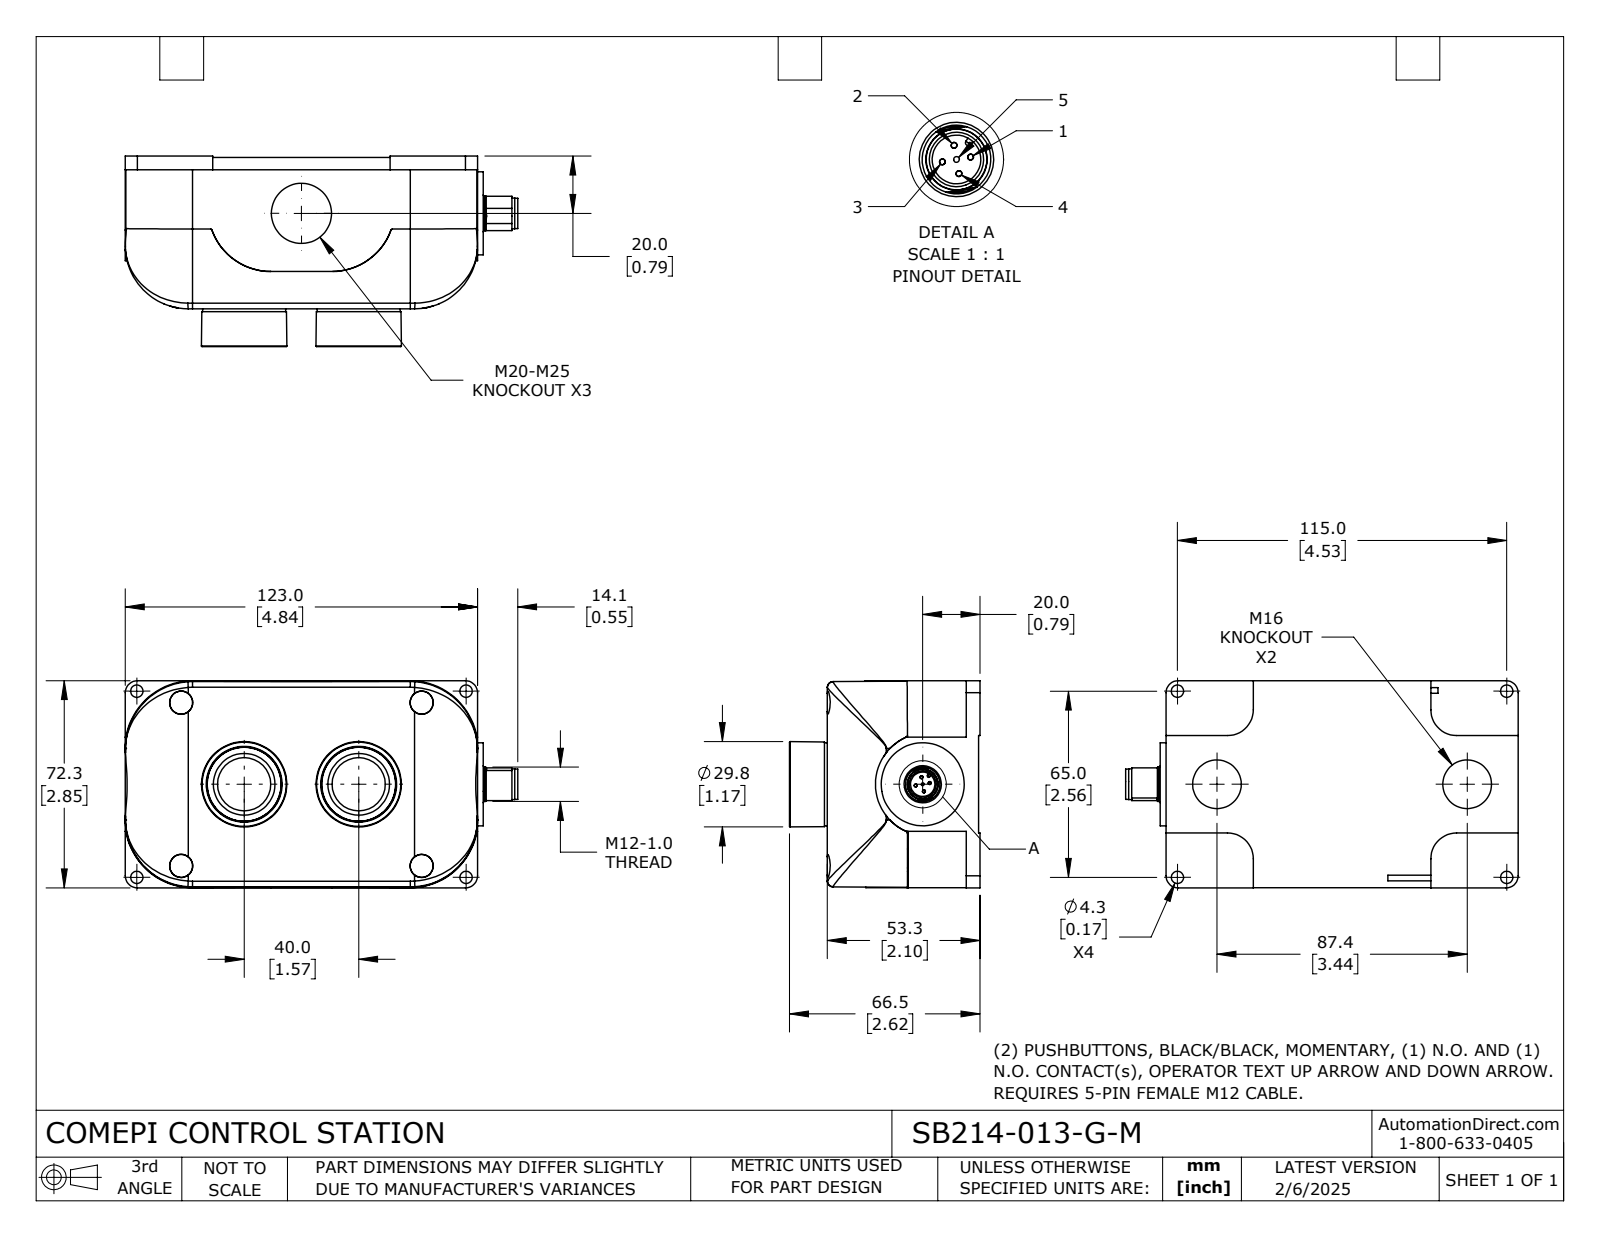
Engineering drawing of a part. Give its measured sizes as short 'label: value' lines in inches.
name: SB214-013-G-M
written by: SolidWorks 2024 (CONFIG_CONTROL_DESIGN)
unit: in
bodies: 14 solids, 665 faces (255 planar, 235 cylindrical, 175 other)
size: 5.396 × 2.846 × 2.618
volume: 16.54 in³; area: 129.7 in²
holes: 4× ⌀0.04, 4× ⌀0.067, 4× ⌀0.087, 4× ⌀0.169, 2× ⌀0.531, 2× ⌀0.669, 2× ⌀0.827, 2× ⌀0.854, 1× ⌀0.335
bosses: 5× ⌀0.039, 4× ⌀0.085, 4× ⌀0.065, 3× ⌀1.142, 2× ⌀1.016, 2× ⌀0.748, 2× ⌀0.63, 2× ⌀0.614
rounds: 5× R0.02, 4× R0.01, 4× R0.035, 4× R0.079, 4× R0.157, 4× R0.354, 4× R0.38, 4× R0.866
face distances: 0.098, 2.079, 1.98, 0.118, 0.976, 0.878, 1.102, 2.098, 0.02, 2.618
hole spacings: 1.39, 1.954, 3.309, 4.185, 0.098, 0.139, 0.139, 0.933
